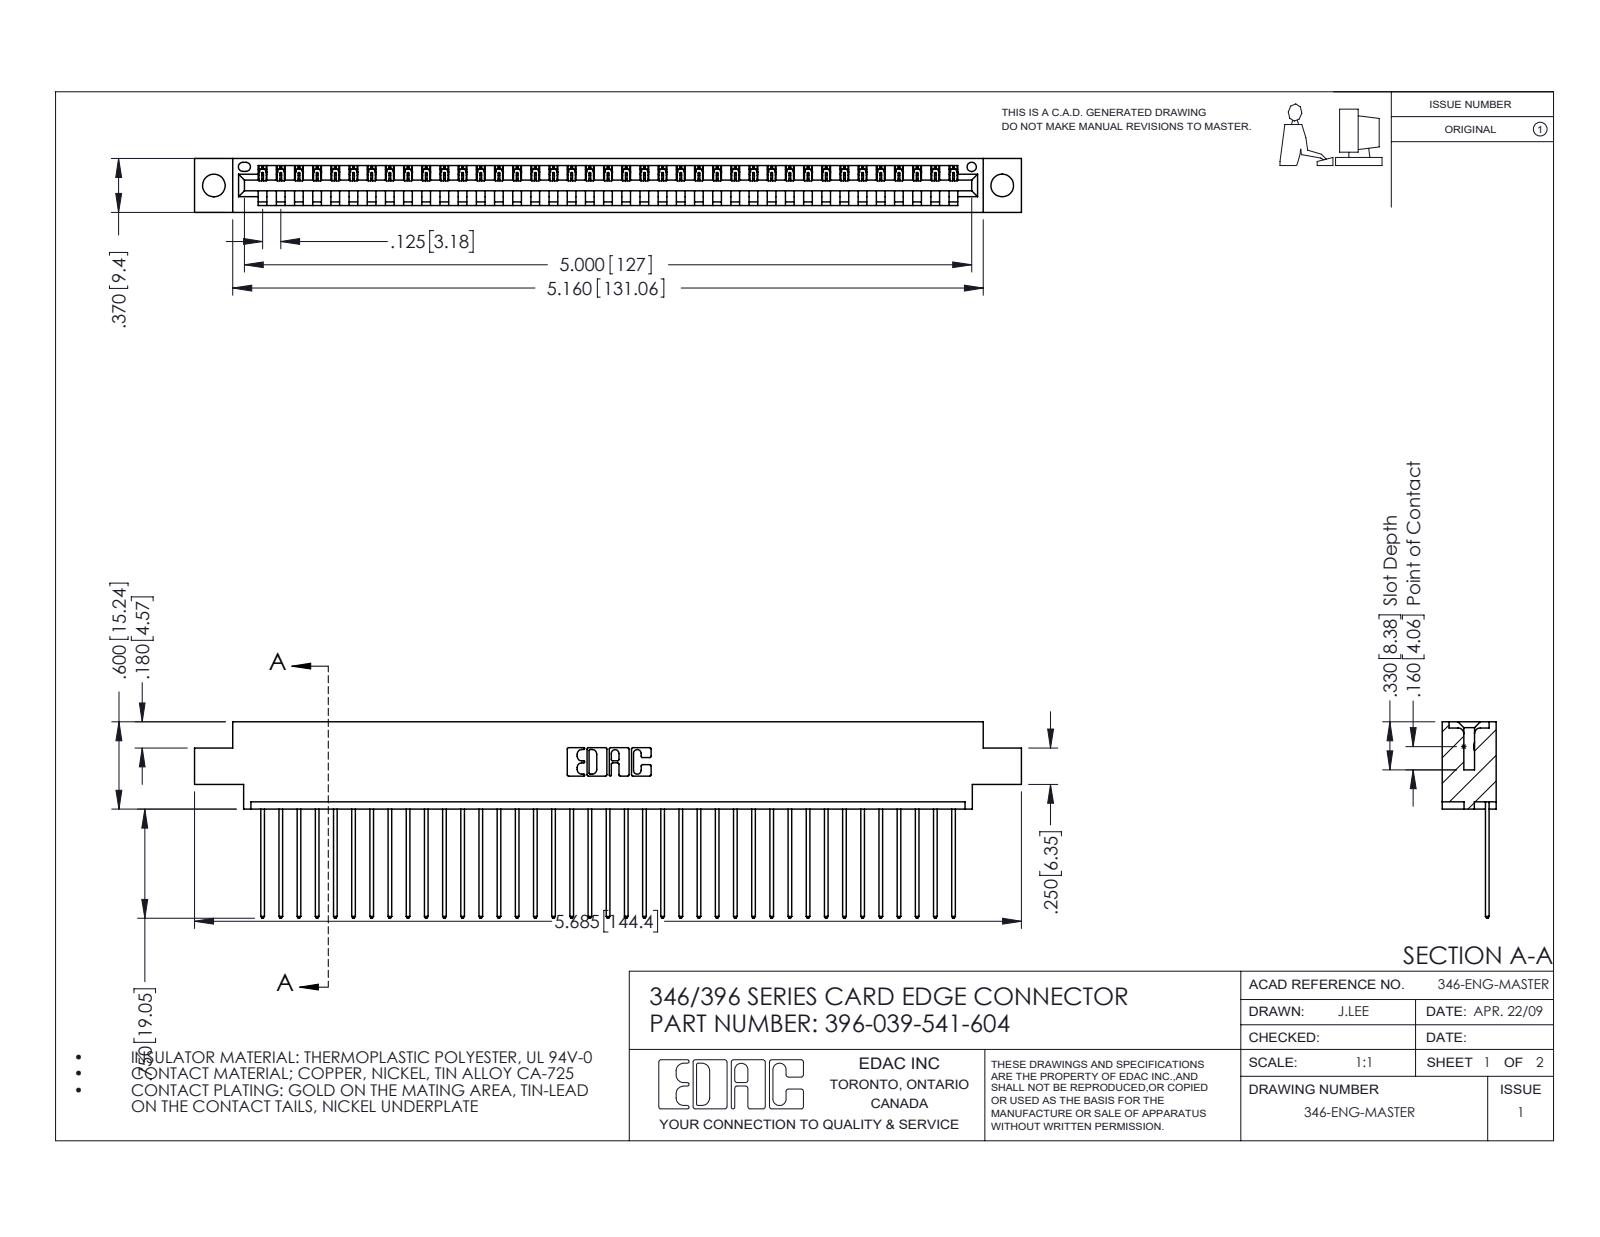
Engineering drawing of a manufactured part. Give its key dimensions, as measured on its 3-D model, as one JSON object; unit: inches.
{"part_name": "346 Part_0.170 Offset - 0.156 Dia-TH; 396-039-541-604; 345-292-001_345-293-141", "step_written_by": "SolidWorks 2016 (CONFIG_CONTROL_DESIGN)", "units": "inches", "bodies": {"solids": 40, "faces": 2388, "planar": 1640, "cylindrical": 748, "other": 0}, "overall_size": [5.685, 1.35, 0.37], "volume_in3": 0.835, "surface_area_in2": 27.6, "round_holes": [[0.156, 2], [0.064, 1]], "partial_cylinders_radius": [[0.006, 78], [0.01, 78], [0.01, 22], [0.007, 6], [0.031, 6], [0.026, 3], [0.031, 2], [0.04, 2]], "face_to_face_distances": [0.048, 0.322, 0.37, 0.25, 0.072, 0.298, 0.025, 0.148, 0.222, 0.1], "hole_center_spacings": [0.246, 5.211, 5.42]}
